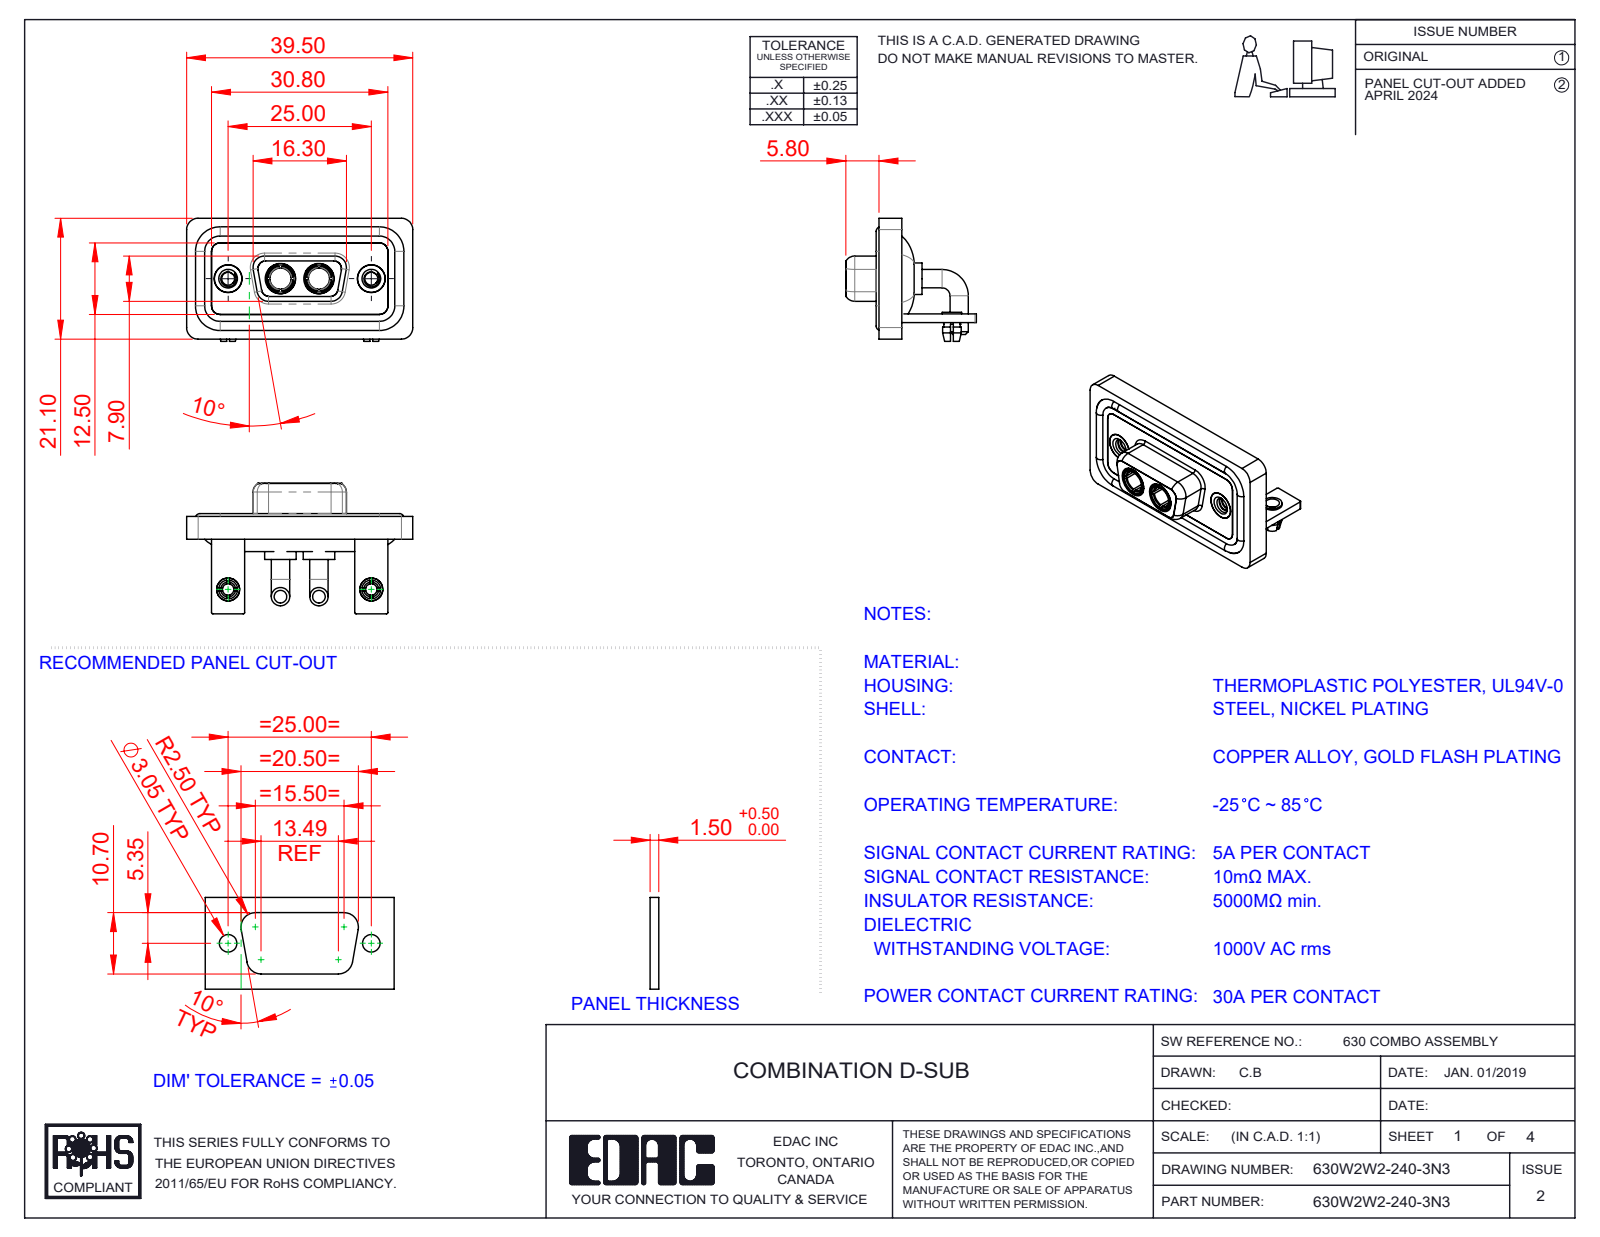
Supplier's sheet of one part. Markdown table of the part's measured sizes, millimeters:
| quantity | value |
| --- | --- |
| part name | 630Combo Shell Rear_09 Contacts; 630Combo Housing_2W2; 630Combo Threaded Rivet_2; 630W2W2-140-3N3 (+5 more) |
| STEP written by | SolidWorks 2023 (CONFIG_CONTROL_DESIGN) |
| units | millimeters |
| bodies | 15 solids, 682 faces (231 planar, 294 cylindrical, 157 other) |
| overall size | 39.5 × 22.8 × 21.5 |
| volume | 5 275 mm³ |
| surface area | 8 768 mm² |
| round holes (diameter × count) | 4.85 × 4, 2 × 2, 2.26 × 2, 2.5 × 2, 3.2 × 2, 3.7 × 2, 4 × 2, 4.05 × 2, 5 × 2, 5.3 × 2 |
| round bosses / shafts (diameter × count) | 3.2 × 4, 1.6 × 4, 5.5 × 2, 5.2 × 2, 4.96 × 2, 4.95 × 2, 4.8 × 2, 4.75 × 2 |
| partial cylindrical surfaces (radius × count) | 2 × 19, 1.5 × 18, 0.25 × 16, 1.35 × 8, 1.6 × 8, 0.5 × 5, 0.6 × 4, 0.65 × 4 |
| main face-to-face distances | 0.4, 2.9, 1.5, 1.8, 1.1, 3.7, 0.8, 2.5, 1.6, 3.1 |
| hole center spacings | 9.14, 15.86, 25, 6.72 |
